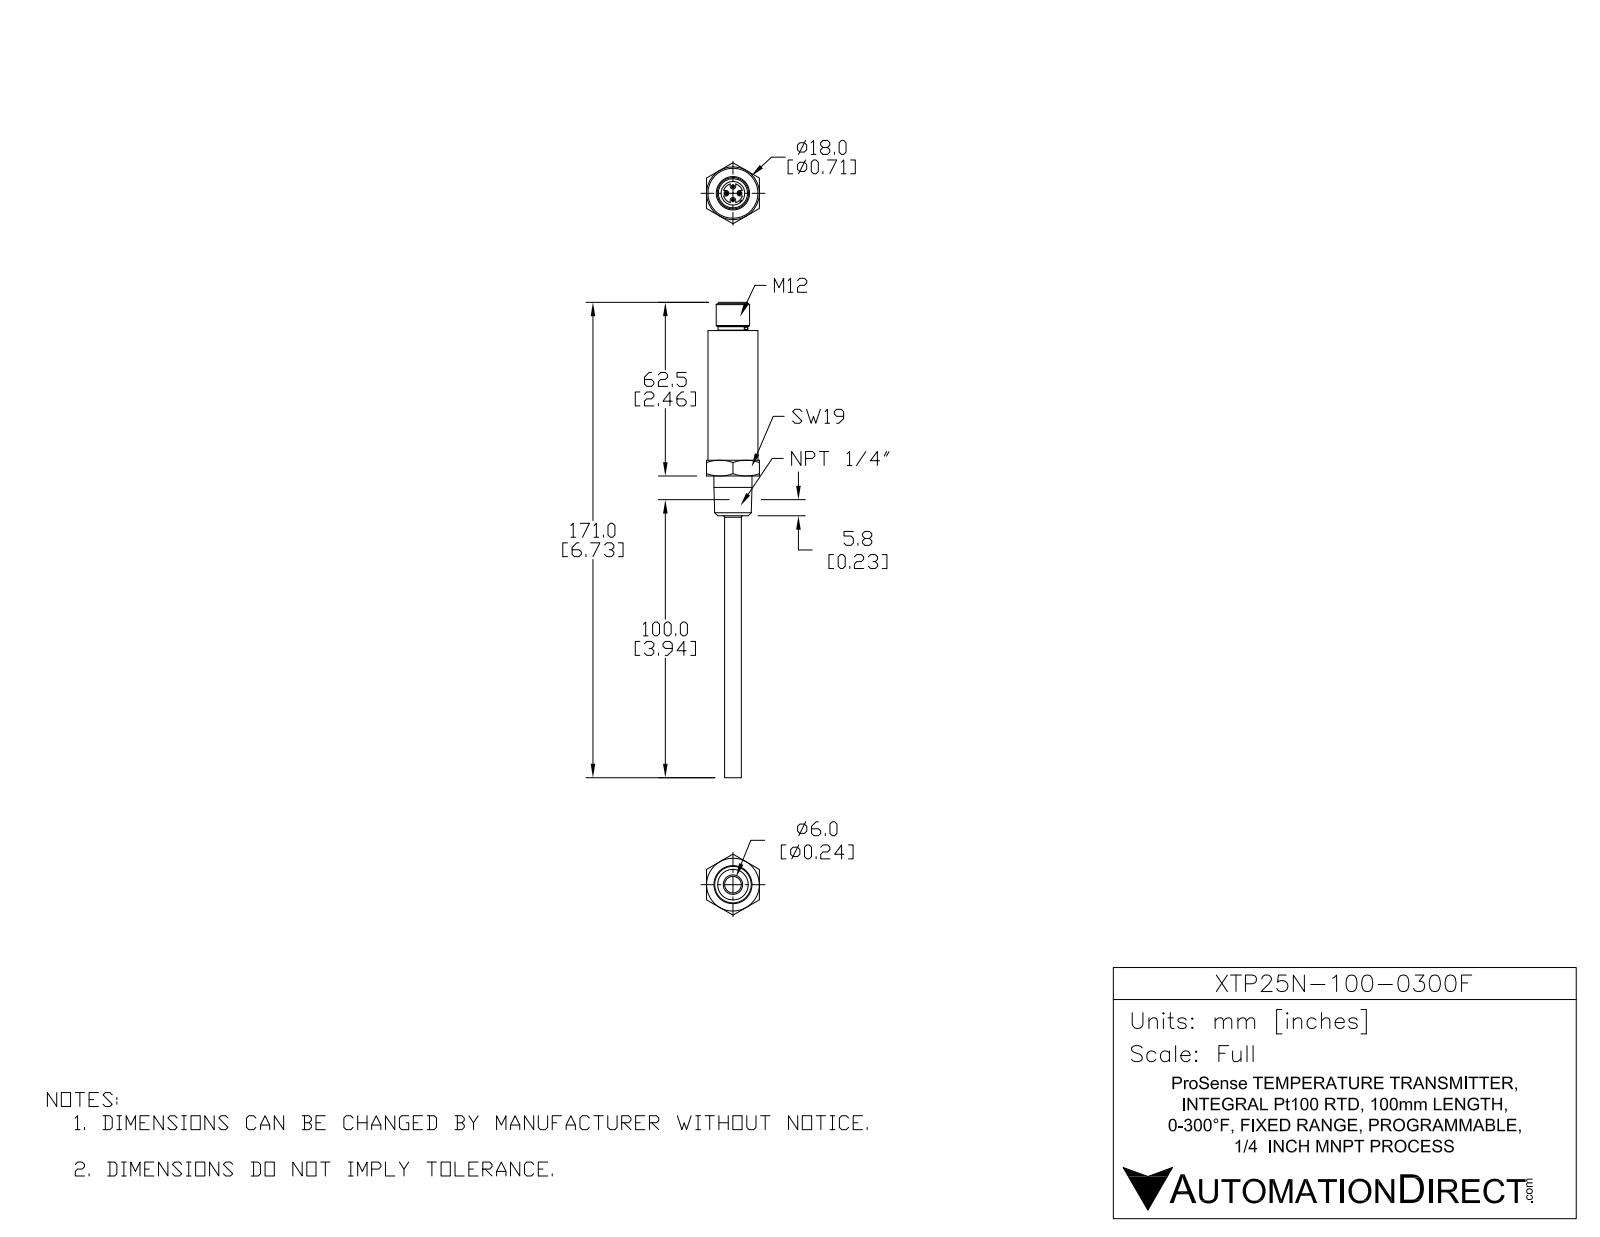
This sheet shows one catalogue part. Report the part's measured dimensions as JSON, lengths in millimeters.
{"part_name": "XTP25N-100-0300F", "step_written_by": "SolidWorks 2015 (AUTOMOTIVE_DESIGN)", "units": "millimeters", "bodies": {"solids": 1, "faces": 117, "planar": 43, "cylindrical": 34, "other": 40}, "overall_size": [171, 21.94, 19], "volume_mm3": 18646, "surface_area_mm2": 6946, "round_holes": [[4, 1], [8.5, 1]], "round_bosses_or_shafts": [[1.02, 4], [18, 1], [13.72, 1], [12, 1], [10.7, 1], [10.5, 1], [6, 1]], "partial_cylinders_radius": [[1, 4], [3.5, 1], [4.25, 1]], "face_to_face_distances": [19, 52.3, 14.3, 66.6, 20, 5.7, 46.6, 76.8, 62.5, 56.8]}
